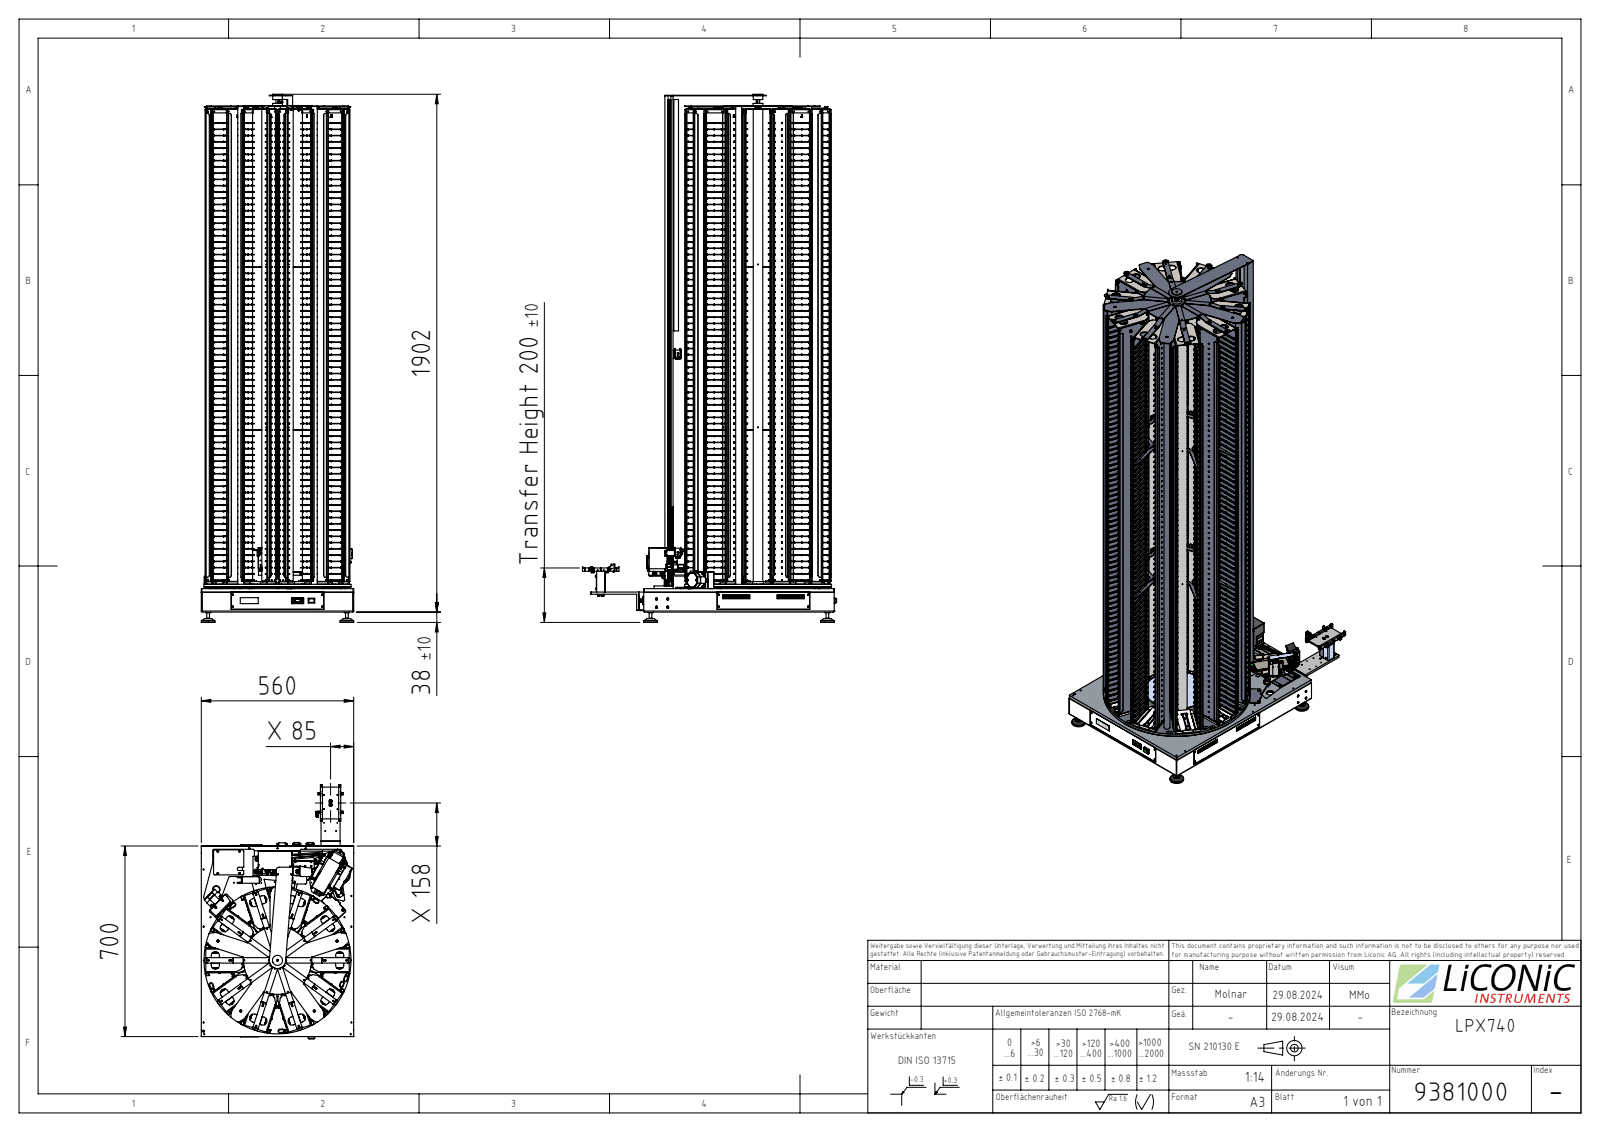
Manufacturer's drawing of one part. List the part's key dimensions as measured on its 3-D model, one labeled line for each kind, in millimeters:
Part name (STEP PRODUCT): 9381000
STEP written by: SolidWorks 2022 (AUTOMOTIVE_DESIGN)
Units: millimetres
Bodies: 64 solids, 9203 faces (4713 planar, 4361 cylindrical, 129 other)
Overall size (bounding box): 1936.3 × 933.98 × 560.01
Volume: 13 870 000 mm³ · Surface area: 5 331 000 mm²
Round holes (diameter × count): ⌀4 ×178, ⌀2.5 ×79, ⌀3.3 ×57, ⌀4.2 ×55, ⌀4.4 ×30, ⌀6.5 ×21, ⌀3 ×20, ⌀7.1 ×16, ⌀8 ×13, ⌀3.4 ×10, ⌀6.2 ×10, ⌀3.1 ×8
Round bosses / shafts (diameter × count): ⌀22 ×5, ⌀50.01 ×4, ⌀10 ×4, ⌀1.5 ×3, ⌀540 ×1, ⌀234 ×1, ⌀15.5 ×1, ⌀14.5 ×1
Partial cylindrical surfaces — rounded edges, fillets, slot ends (radius × count): R0.1 ×832, R0.25 ×832, R2 ×675, R1 ×136, R5 ×121, R2.5 ×114, R3 ×66, R1.7 ×40
Main face-to-face distances: 2, 1, 72, 74, 89.99, 12, 6, 86, 84, 10
Hole centre spacings: 23, 46, 69, 92, 115, 138, 161, 184
